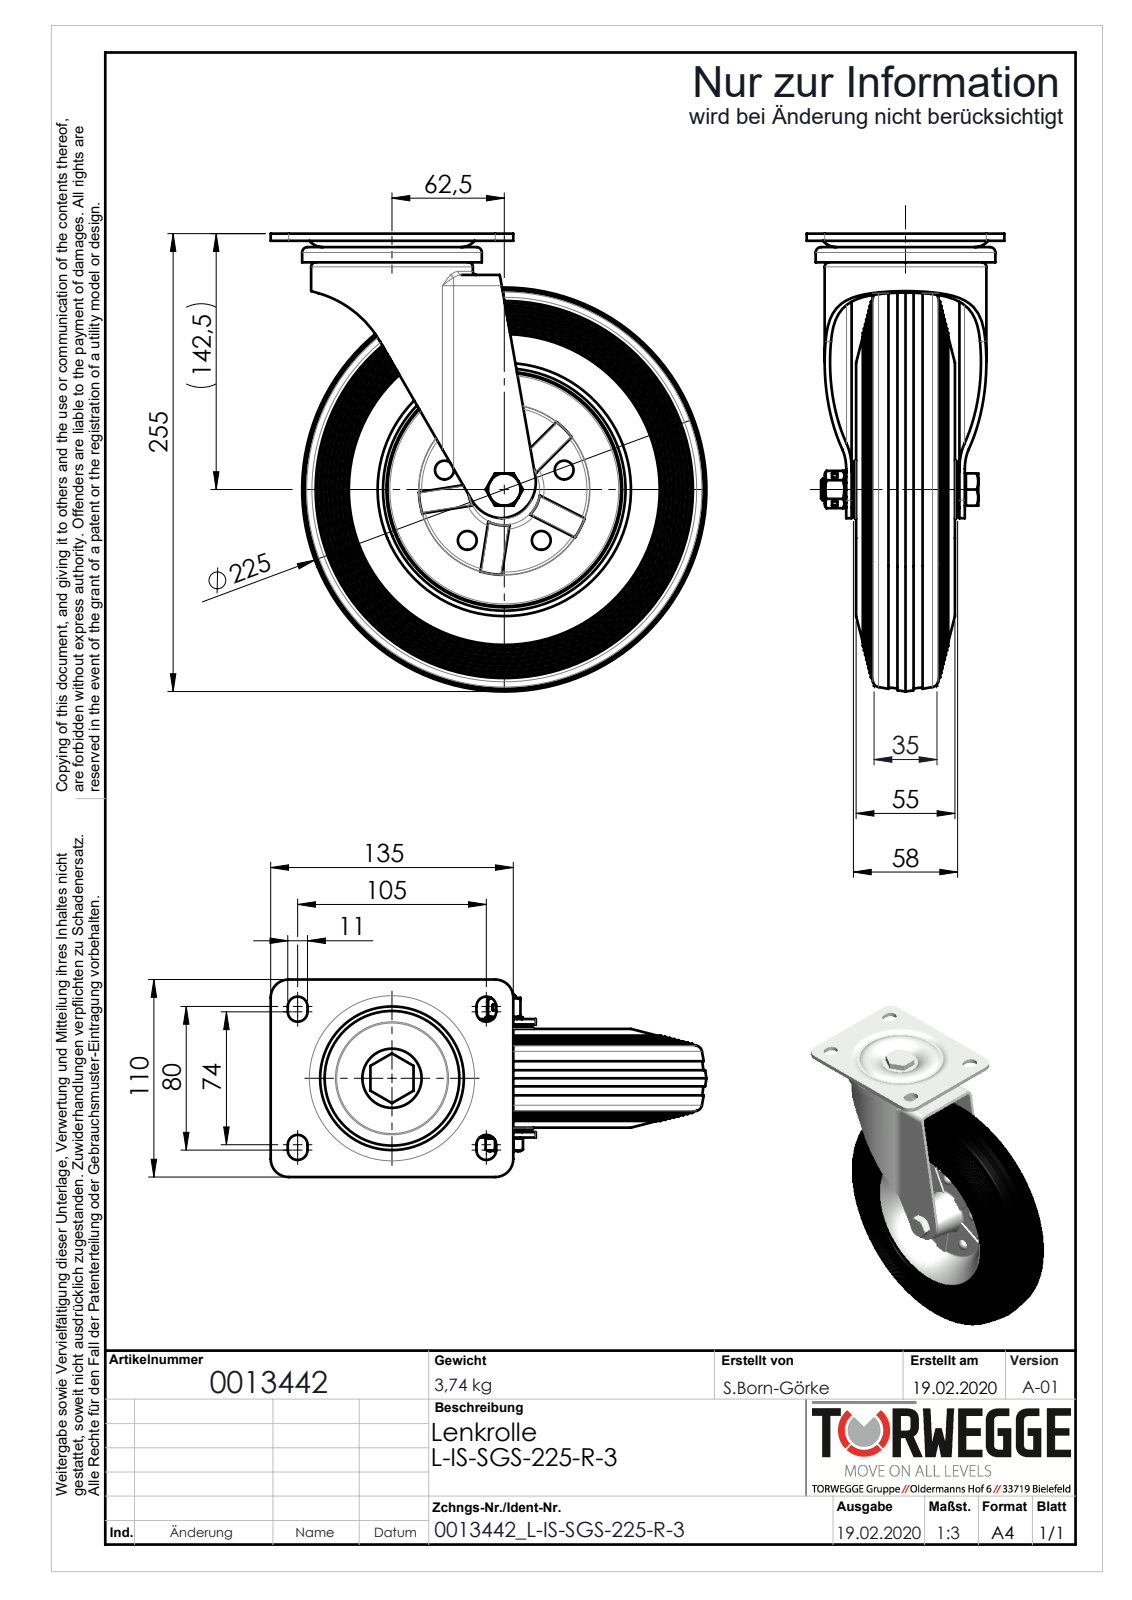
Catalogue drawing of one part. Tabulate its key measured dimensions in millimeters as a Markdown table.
| quantity | value |
| --- | --- |
| part name | 0013442_L-IS-SGS-225-R-3_(A-01) |
| STEP written by | SolidWorks 2018 (AUTOMOTIVE_DESIGN) |
| units | millimeters |
| bodies | 14 solids, 640 faces (174 planar, 134 cylindrical, 332 other) |
| overall size | 255 × 242.5 × 110 |
| volume | 1 549 000 mm³ |
| surface area | 296 395 mm² |
| round holes (diameter × count) | 6 × 5, 10.2 × 1, 12 × 1, 12.5 × 1, 20 × 1, 21.5 × 1, 84 × 1, 94 × 1 |
| round bosses / shafts (diameter × count) | 100 × 1, 90 × 1, 30 × 1, 20.5 × 1, 18 × 1 |
| partial cylindrical surfaces (radius × count) | 0.5 × 20, 5.5 × 8, 20 × 7, 10 × 6, 47.5 × 5, 3 × 2, 6 × 2, 13 × 2 |
| main face-to-face distances | 3, 30, 33, 63, 4, 1, 32, 29, 10.5, 34 |
| hole center spacings | 35.03, 41.18, 66.64, 35.04, 41.19, 66.63 |
